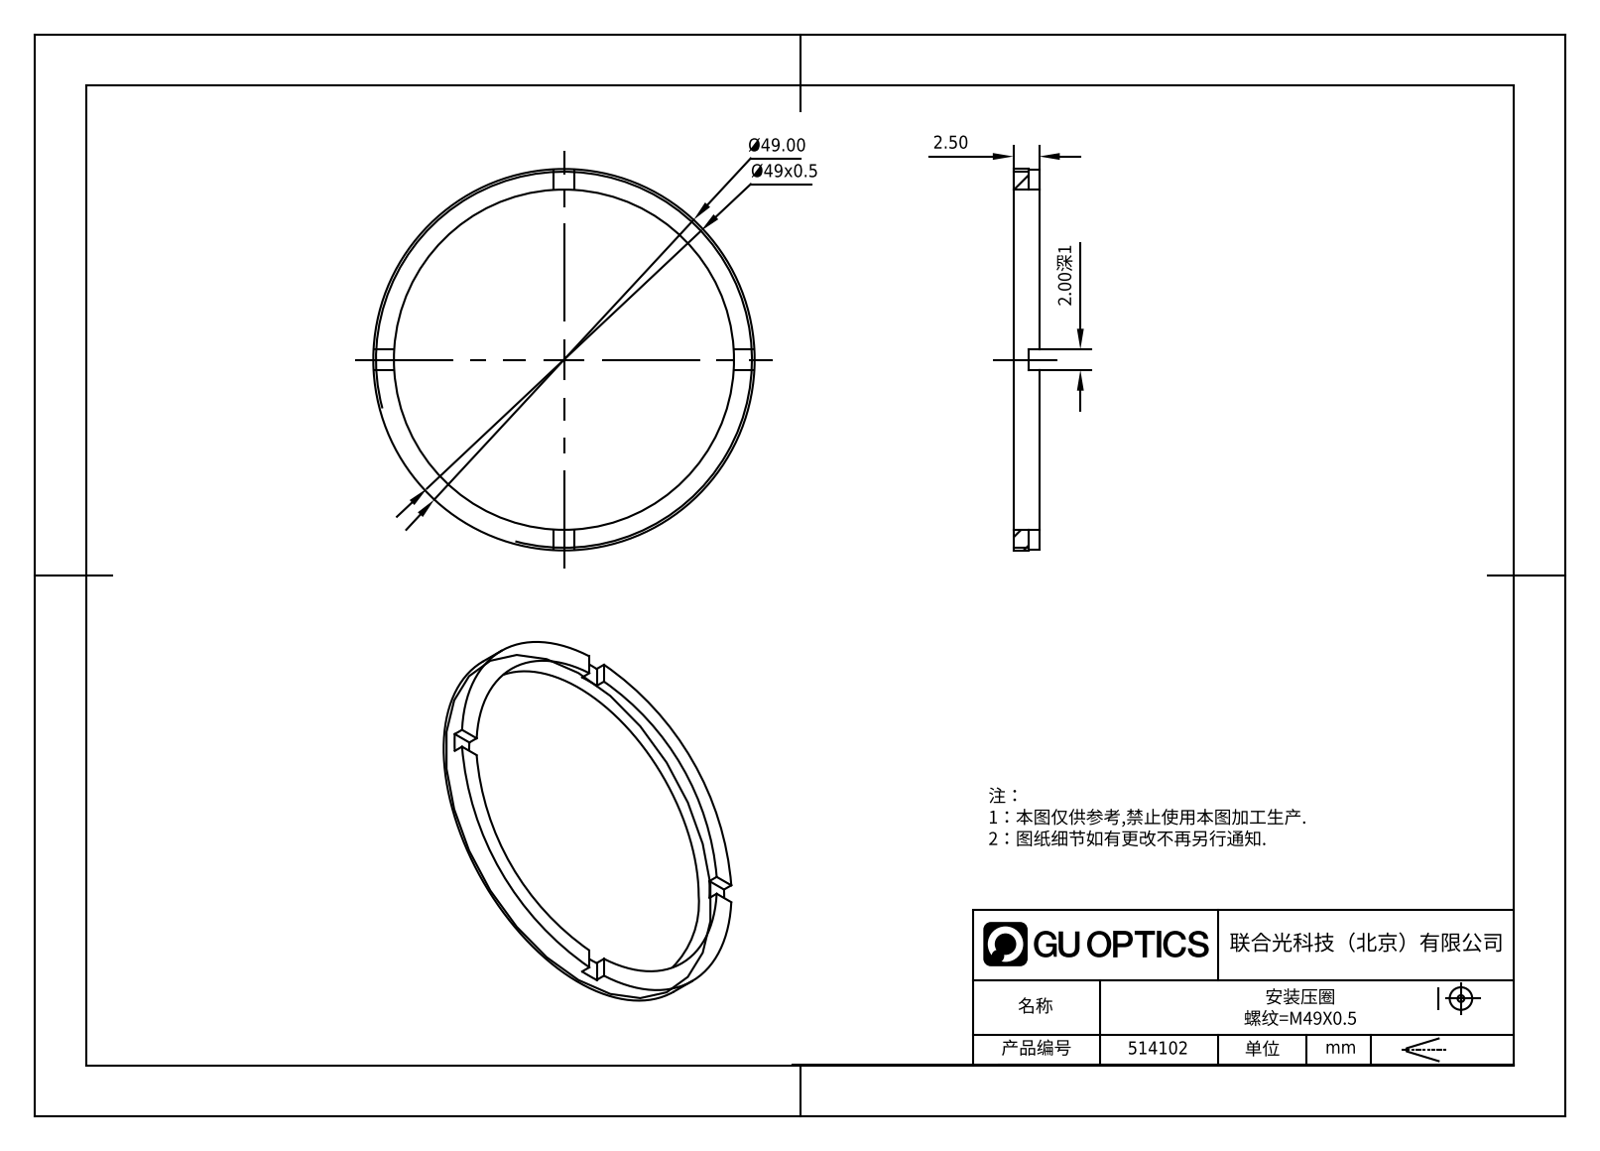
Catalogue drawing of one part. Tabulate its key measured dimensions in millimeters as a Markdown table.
| quantity | value |
| --- | --- |
| part name | 514102 |
| STEP written by | SolidWorks 2020 (CONFIG_CONTROL_DESIGN) |
| units | millimeters |
| bodies | 1 solid, 21 faces (17 planar, 4 cylindrical, 0 other) |
| overall size | 49 × 49 × 2.5 |
| volume | 722 mm³ |
| surface area | 1 329 mm² |
| round holes (diameter × count) | 45 × 1 |
| round bosses / shafts (diameter × count) | 49 × 1 |
| main face-to-face distances | 2.5, 1.5, 1, 2 |
